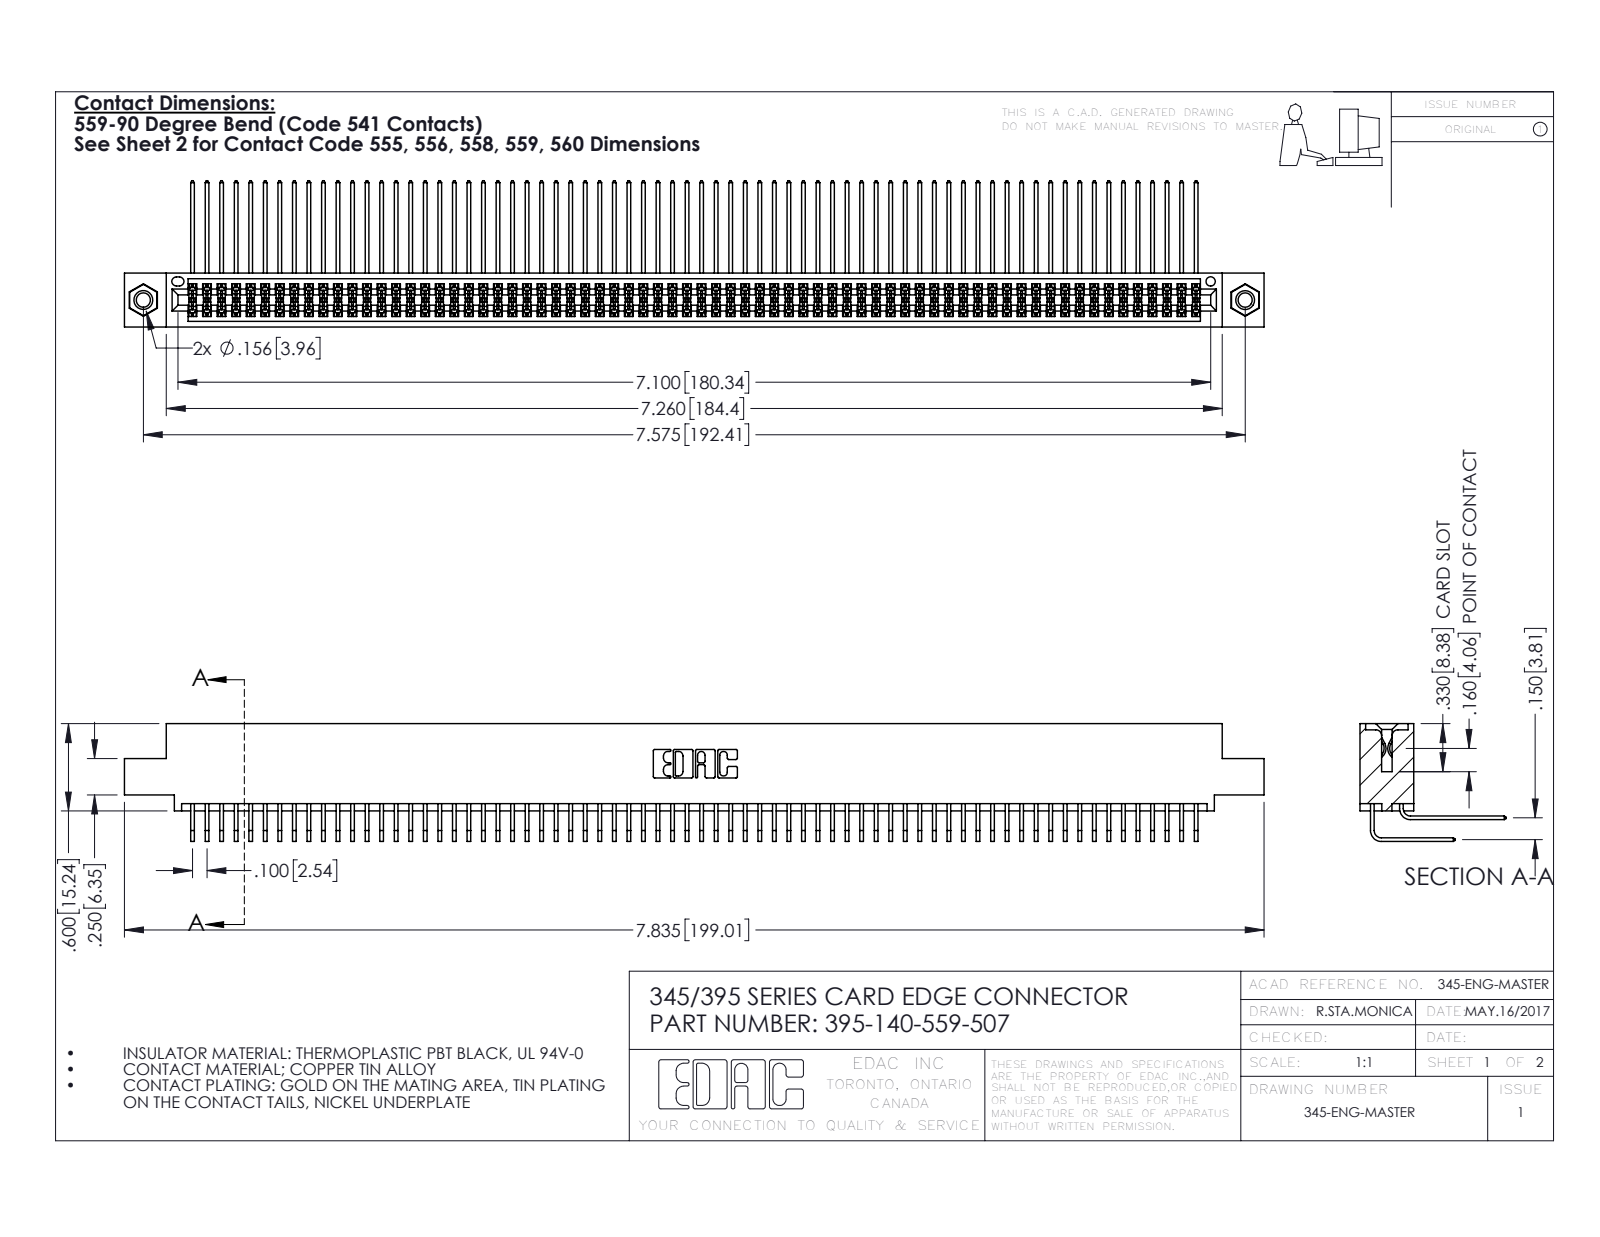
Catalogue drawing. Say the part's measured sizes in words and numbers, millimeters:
The part is named "345 Part_0.110 Offset - 0.156 Dia-TI; 345-292-001_558 559 Tail - 1; 345-292-001_559 Tail - 2; 395-140-559-507 (+1 more)". Its 3-D file was written by "SolidWorks 2016 (CONFIG_CONTROL_DESIGN)". It is 143 solids with 7470 faces: 5016 planar, 2438 cylindrical and 16 other. Overall it measures 199 by 25.5 by 20.5 millimeters. Its volume is 20 320 cubic millimeters and its surface area 34 480 square millimeters. Round holes: 2 of diameter 2.5, 2 of diameter 3.2, 2 of diameter 4, 1 of diameter 1.6. Round bosses or shafts: 2 of diameter 3.9. Partial cylindrical surfaces (rounded edges, fillets, slot ends): 279 of radius 0.2, 22 of radius 0.3, 6 of radius 0.2, 6 of radius 0.8, 3 of radius 0.7, 2 of radius 0.4, 2 of radius 0.5, 2 of radius 0.6. The main face-to-face distances are 1.8, 7.6, 5.1, 9.4, 2.5, 6.9, 0.6, 5.7, 4.4, 3.8. The hole center spacings are 6.9, 186.4, 192.4.
